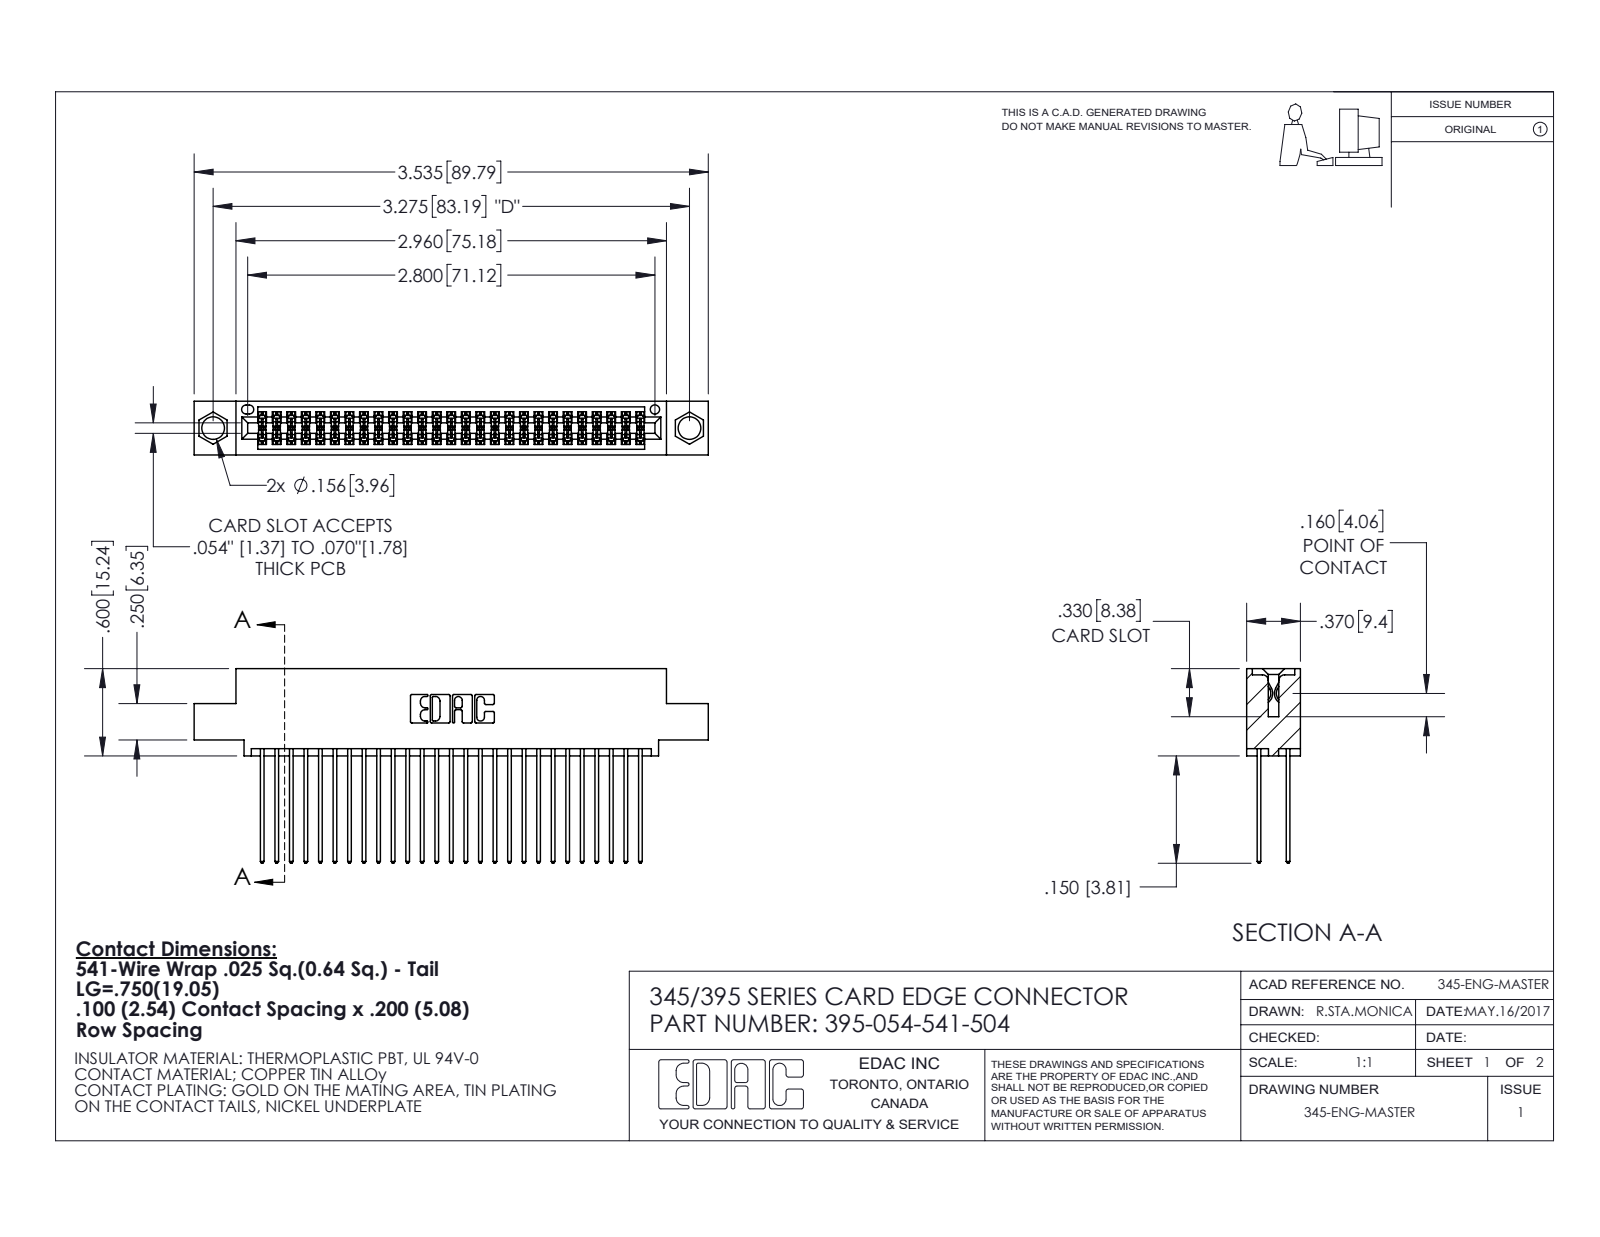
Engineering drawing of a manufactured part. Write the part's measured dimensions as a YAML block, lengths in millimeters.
part_name: "395-054-541-504; 345-292-001_345-293-141; 345 Part_0.110 Offset - 0.156 Dia-TI"
step_written_by: "SolidWorks 2020 (CONFIG_CONTROL_DESIGN)"
units: millimeters
bodies: {solids: 55, faces: 2844, planar: 1880, cylindrical: 964, other: 0}
overall_size: [89.8, 34, 9.4]
volume: 8720
surface_area: 13990
round_holes:
  - {diameter: 4, count: 2}
  - {diameter: 1.6, count: 1}
partial_cylinders:
  - {radius: 0.2, count: 108}
  - {radius: 0.3, count: 54}
  - {radius: 0.3, count: 22}
  - {radius: 0.2, count: 6}
  - {radius: 0.8, count: 6}
  - {radius: 0.7, count: 3}
  - {radius: 0.4, count: 2}
  - {radius: 0.5, count: 2}
face_to_face_distances: [1.8, 7.6, 5.1, 2.5, 6.9, 0.6, 5.7, 9.4, 4.4, 3.8]
hole_center_spacings: [6.9, 77.2, 83.2]
